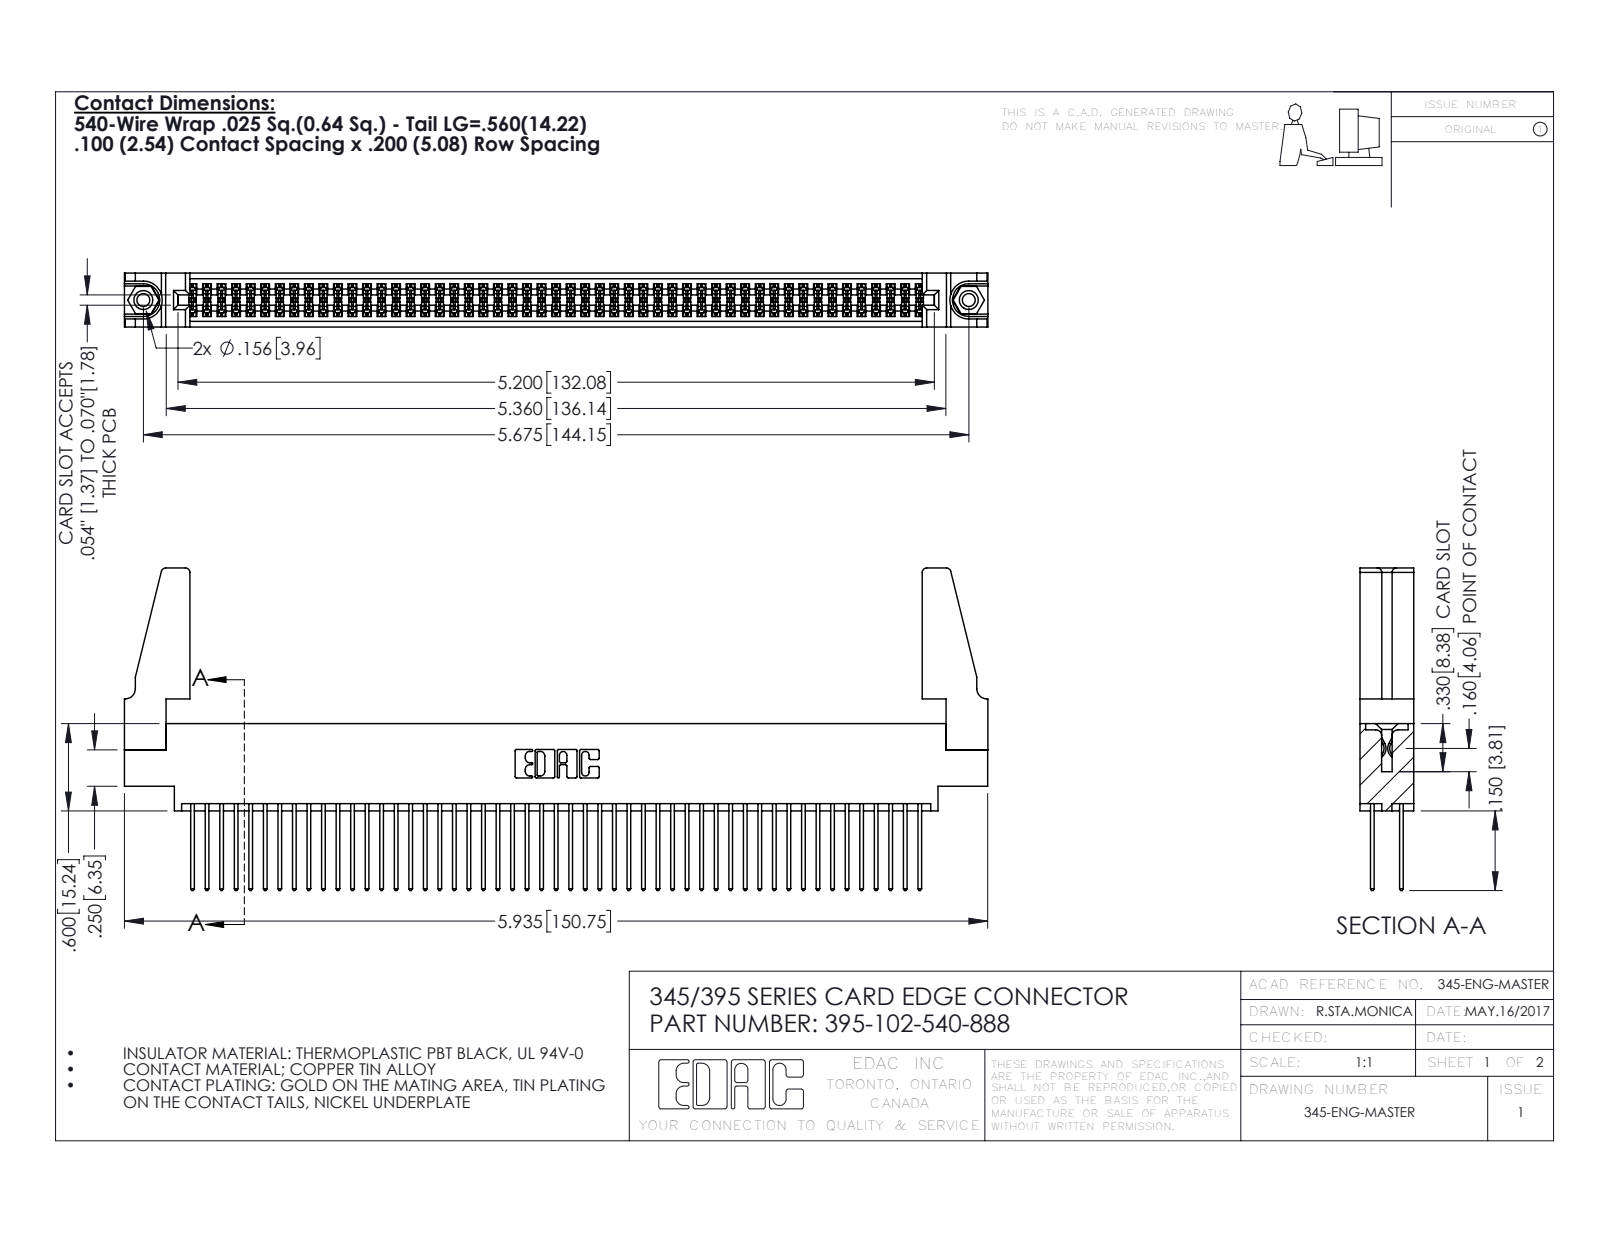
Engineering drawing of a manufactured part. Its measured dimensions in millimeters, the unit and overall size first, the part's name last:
Units: millimetres
Overall size (bounding box): 150.8 × 56.3 × 9.4
Round holes (diameter × count): ⌀2.3 ×2, ⌀3.2 ×2, ⌀4 ×2, ⌀1.6 ×1
Round bosses / shafts (diameter × count): ⌀3.9 ×2
Partial cylindrical surfaces — rounded edges, fillets, slot ends (radius × count): R0.2 ×153, R0.3 ×102, R0.3 ×22, R0.8 ×8, R0.2 ×6, R0.8 ×6, R0.7 ×3, R0.4 ×2
Main face-to-face distances: 1.8, 7.6, 5.1, 9.4, 2.5, 6.9, 0.6, 5.7, 4.4, 3.8
Hole centre spacings: 6.9, 138.2, 144.1
Volume: 18 260 mm³ · Surface area: 27 410 mm²
Bodies: 107 solids, 5354 faces (3522 planar, 1816 cylindrical, 16 other)
Part name (STEP PRODUCT): 345-292-001_345-293-140; 345-220-078_345-220-088; 345-250-001_345-250-001-102; 395-102-540-888 (+1 more)
STEP written by: SolidWorks 2016 (CONFIG_CONTROL_DESIGN)
